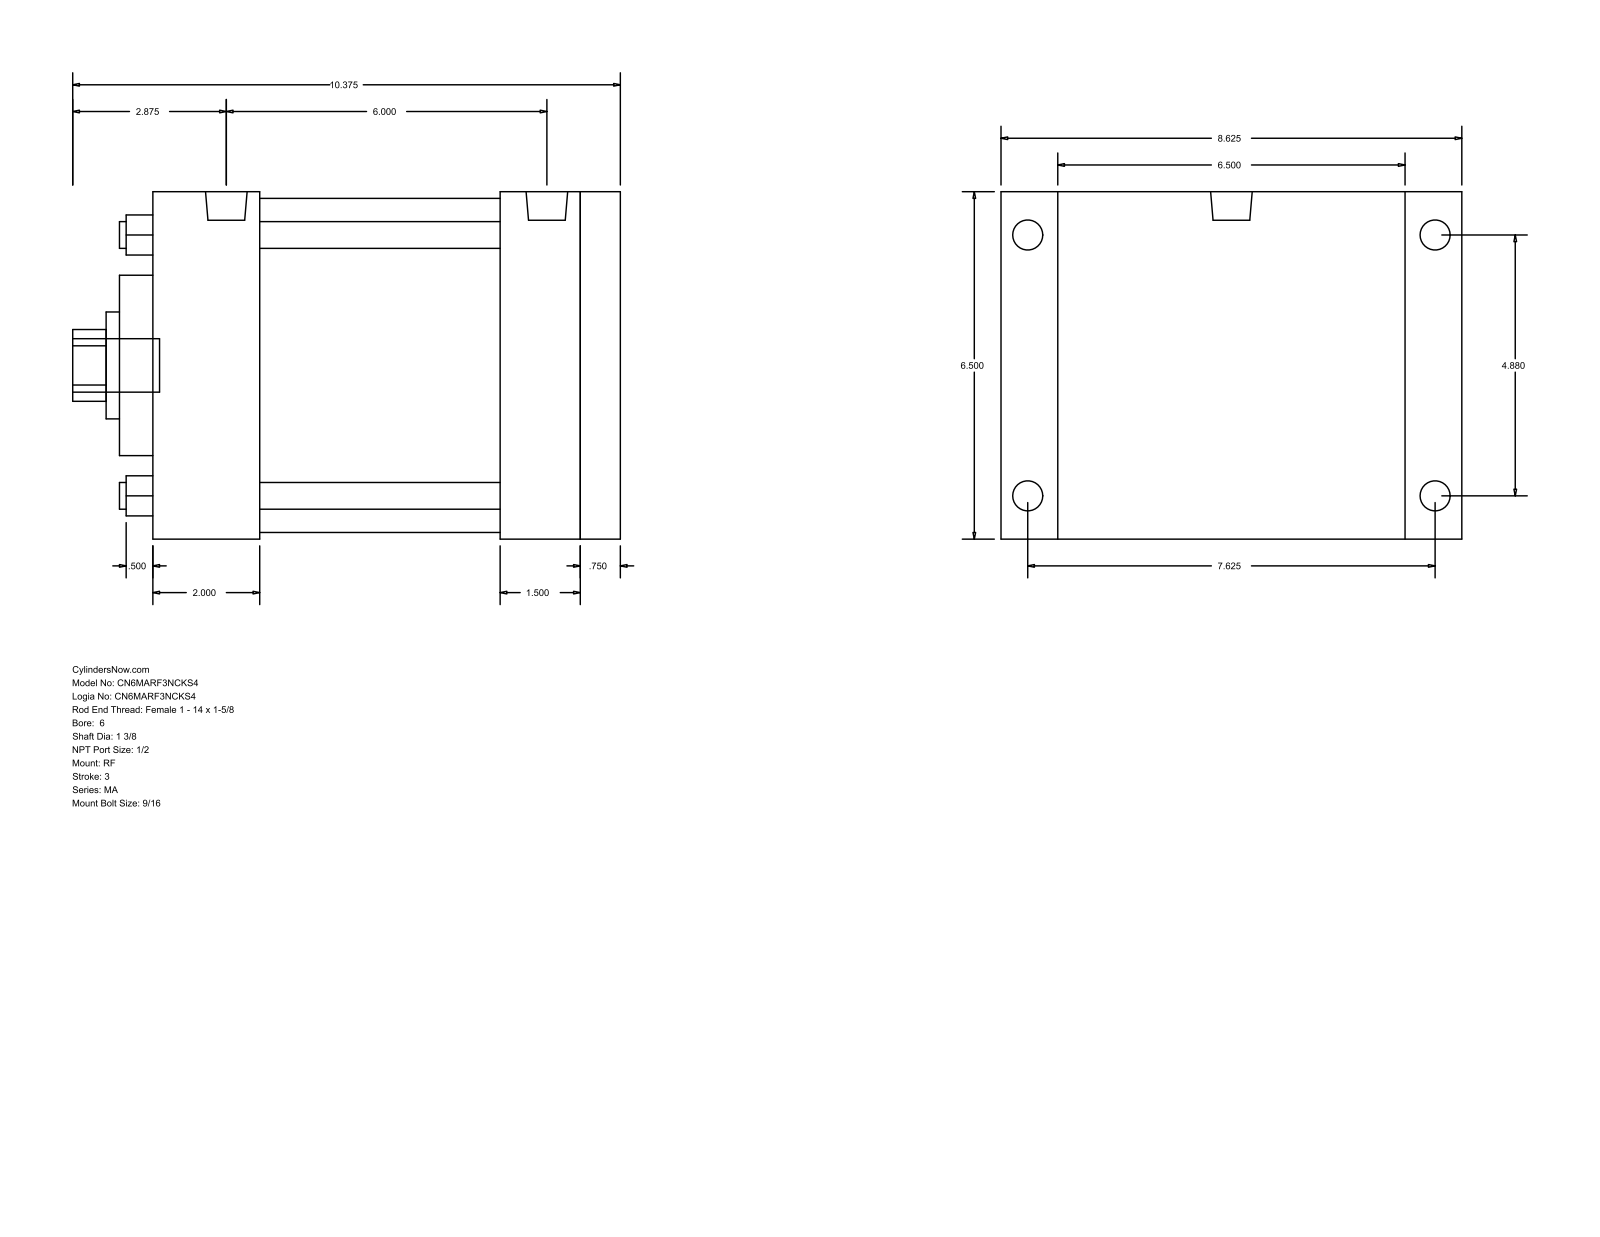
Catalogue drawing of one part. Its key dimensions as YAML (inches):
part_name: "MA_RF__0600_1.375"
step_written_by: "GSSL Pune (CONFIG_CONTROL_DESIGN)"
units: inches
bodies: {solids: 0, faces: 94, planar: 65, cylindrical: 29, other: 0}
overall_size: [10.375, 8.625, 6.5]
round_holes:
  - {diameter: 0.5, count: 4}
  - {diameter: 1.375, count: 1}
  - {diameter: 2, count: 1}
  - {diameter: 3.375, count: 1}
  - {diameter: 6.25, count: 1}
round_bosses_or_shafts:
  - {diameter: 0.687, count: 4}
  - {diameter: 0.563, count: 4}
  - {diameter: 0.778, count: 2}
  - {diameter: 1, count: 1}
partial_cylinders:
  - {radius: 0.672, count: 1}
face_to_face_distances: [6.5, 8.875, 0.75, 8.125, 2, 6.125, 6.875, 6.625, 4.625, 1.5]
hole_center_spacings: [3.451, 4.88, 6.902]
